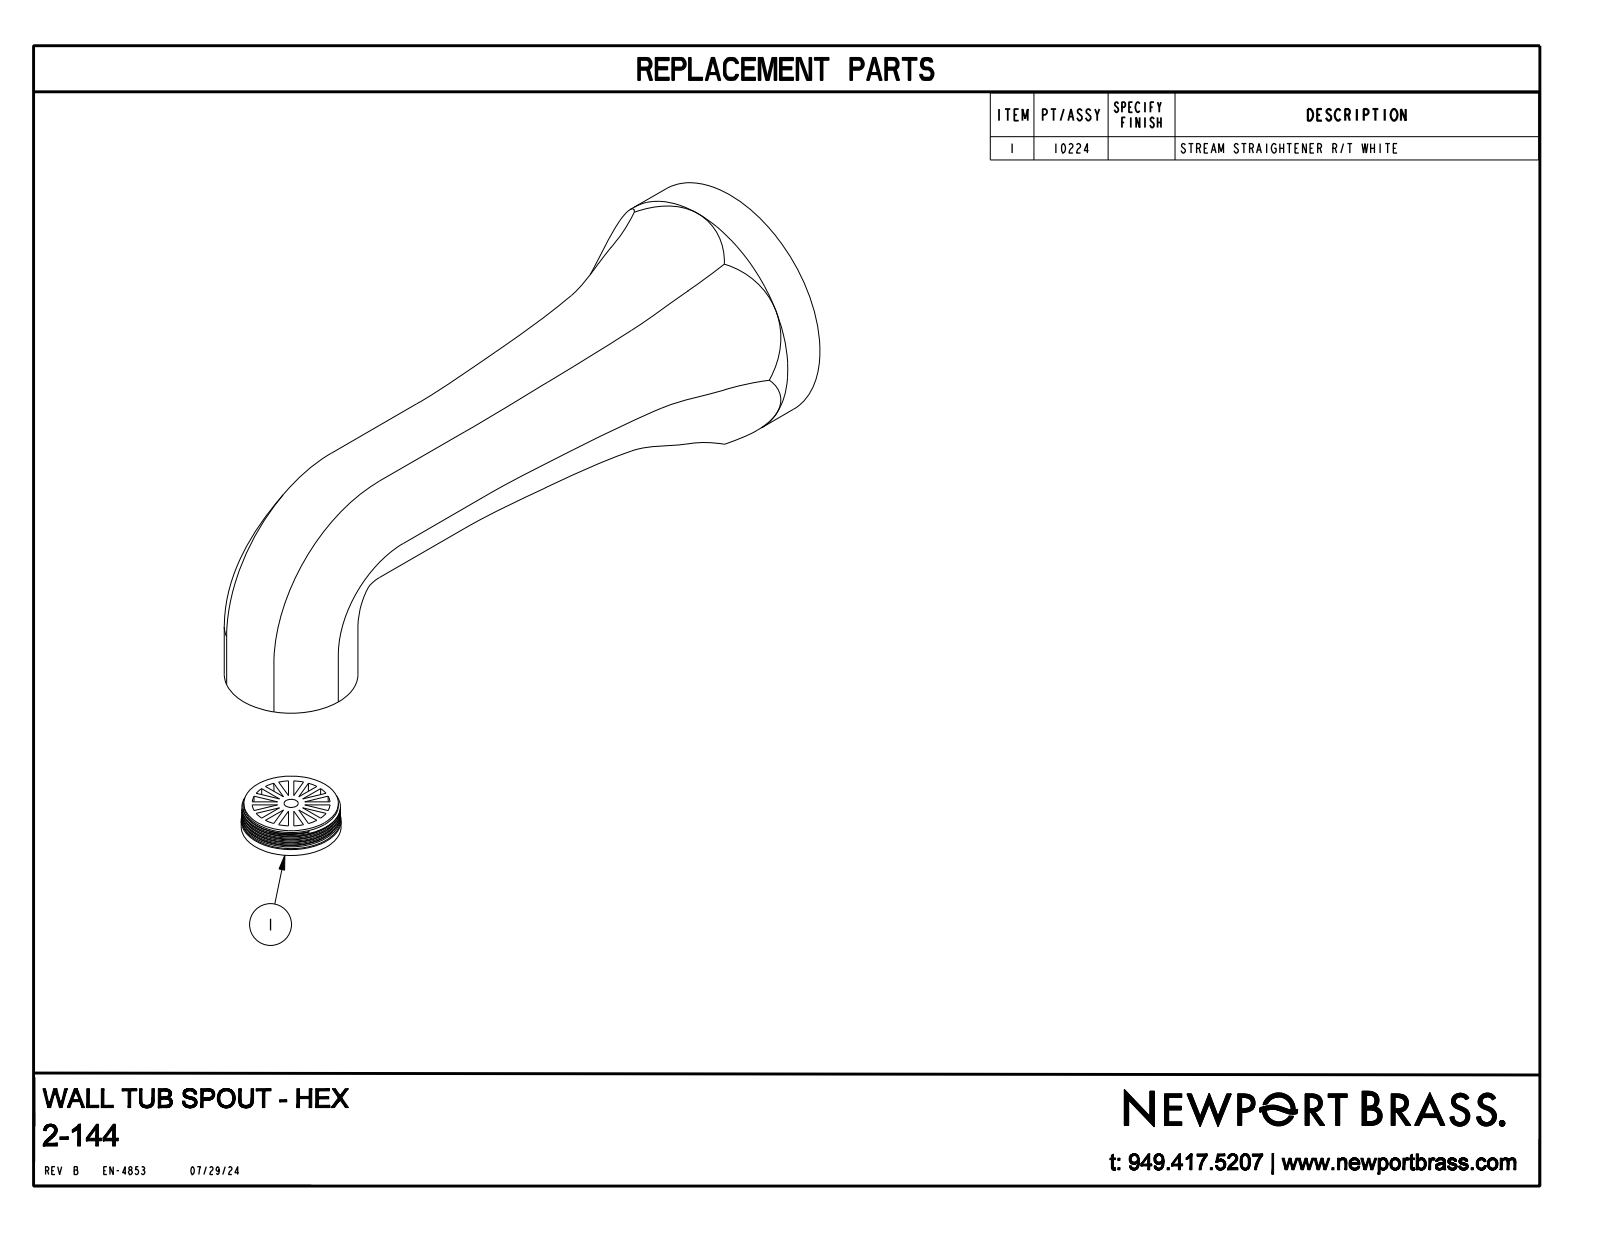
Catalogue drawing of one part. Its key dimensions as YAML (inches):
part_name: "PRT0001"
step_written_by: "CREO PARAMETRIC BY PTC INC, 2018400 (AUTOMOTIVE_DESIGN)"
units: inches
bodies: {solids: 1, faces: 49, planar: 8, cylindrical: 10, other: 31}
overall_size: [7.562, 3.045, 2.8]
volume: 18.75
surface_area: 52.24
round_bosses_or_shafts:
  - {diameter: 2.8, count: 1}
  - {diameter: 1.47, count: 1}
partial_cylinders:
  - {radius: 2.125, count: 6}
face_to_face_distances: [1.299, 2.294, 0.995]
